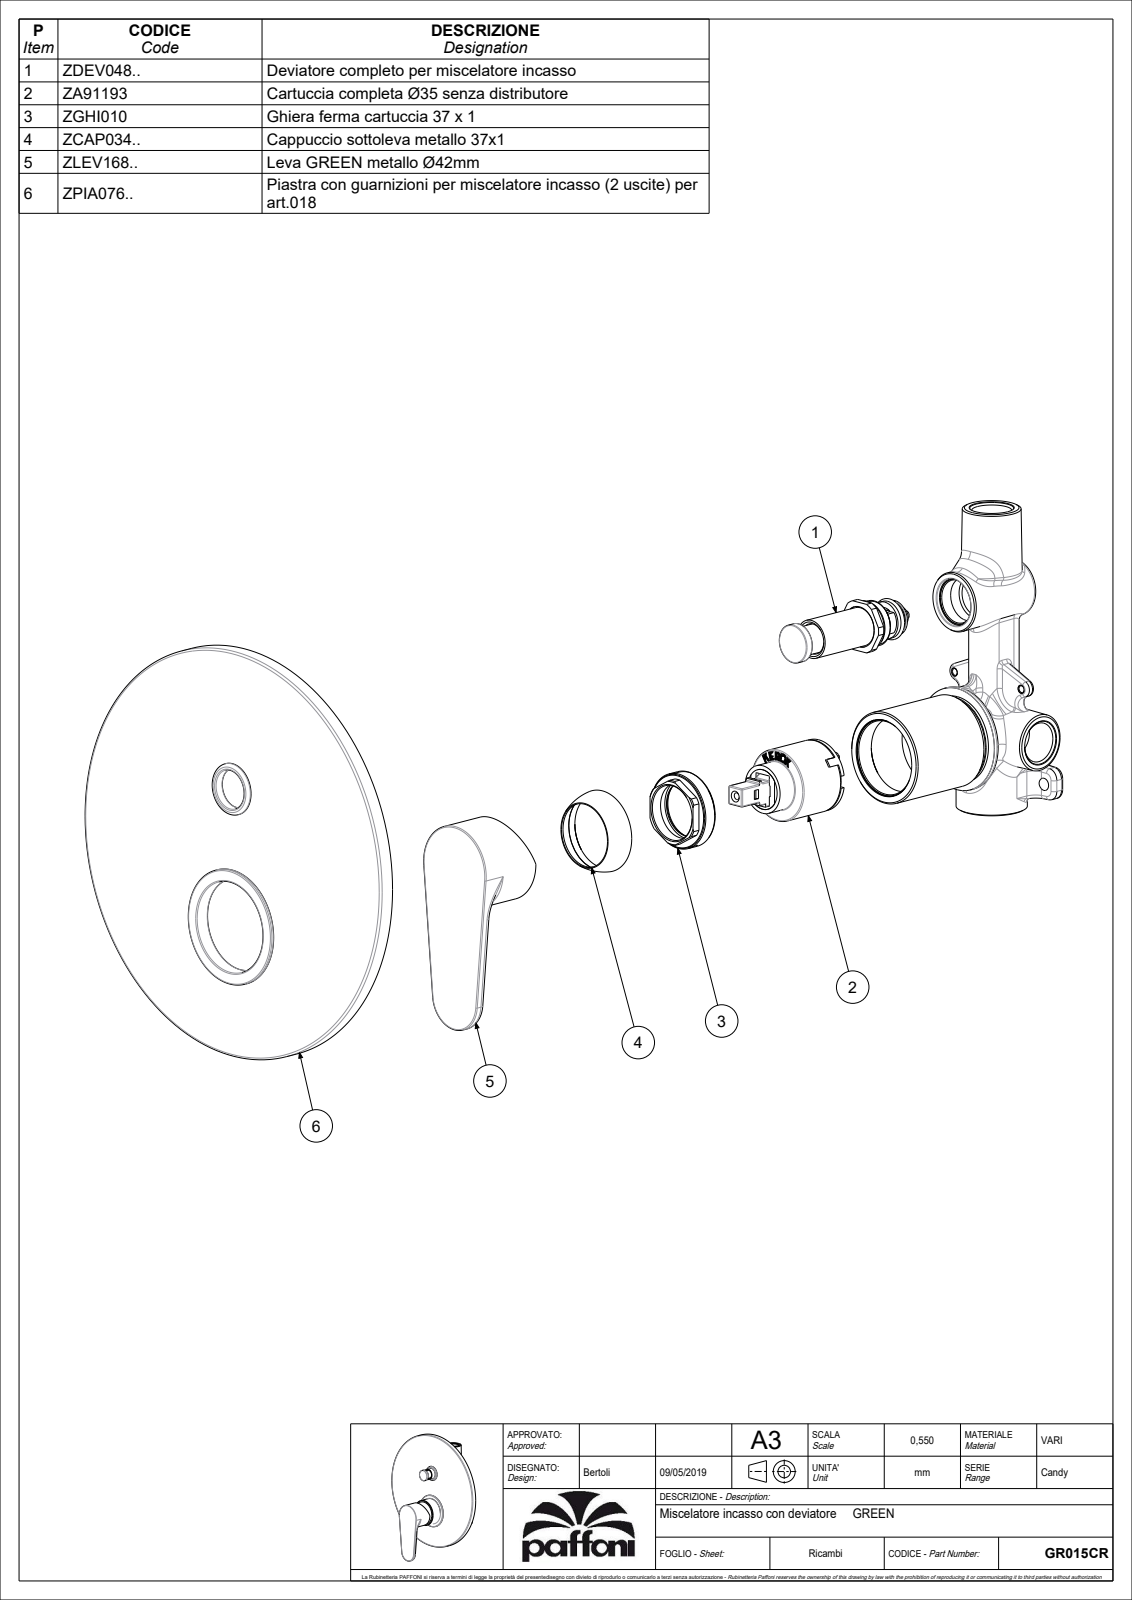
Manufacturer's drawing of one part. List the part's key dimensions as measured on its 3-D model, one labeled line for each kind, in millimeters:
Part name (STEP PRODUCT): GR015CR
STEP written by: CREO PARAMETRIC BY PTC INC, 2020044 (CONFIG_CONTROL_DESIGN)
Units: millimetres
Bodies: 2 solids, 146 faces (50 planar, 53 cylindrical, 43 other)
Overall size (bounding box): 215.25 × 200 × 74.8
Volume: 300 637 mm³ · Surface area: 96 272 mm²
Round holes (diameter × count): ⌀3 ×1, ⌀4.2 ×1, ⌀30.6 ×1, ⌀36 ×1, ⌀37.5 ×1, ⌀39 ×1
Round bosses / shafts (diameter × count): ⌀200 ×1, ⌀56.2 ×1, ⌀44.8 ×1, ⌀42 ×1, ⌀27.7 ×1, ⌀18.7 ×1, ⌀18.6 ×1, ⌀14 ×1
Partial cylindrical surfaces — rounded edges, fillets, slot ends (radius × count): R0.5 ×2, R3 ×2, R15 ×1
Main face-to-face distances: 8, 74.8, 66.8, 2, 10, 64.8, 6, 68.8, 60.8, 58.8
